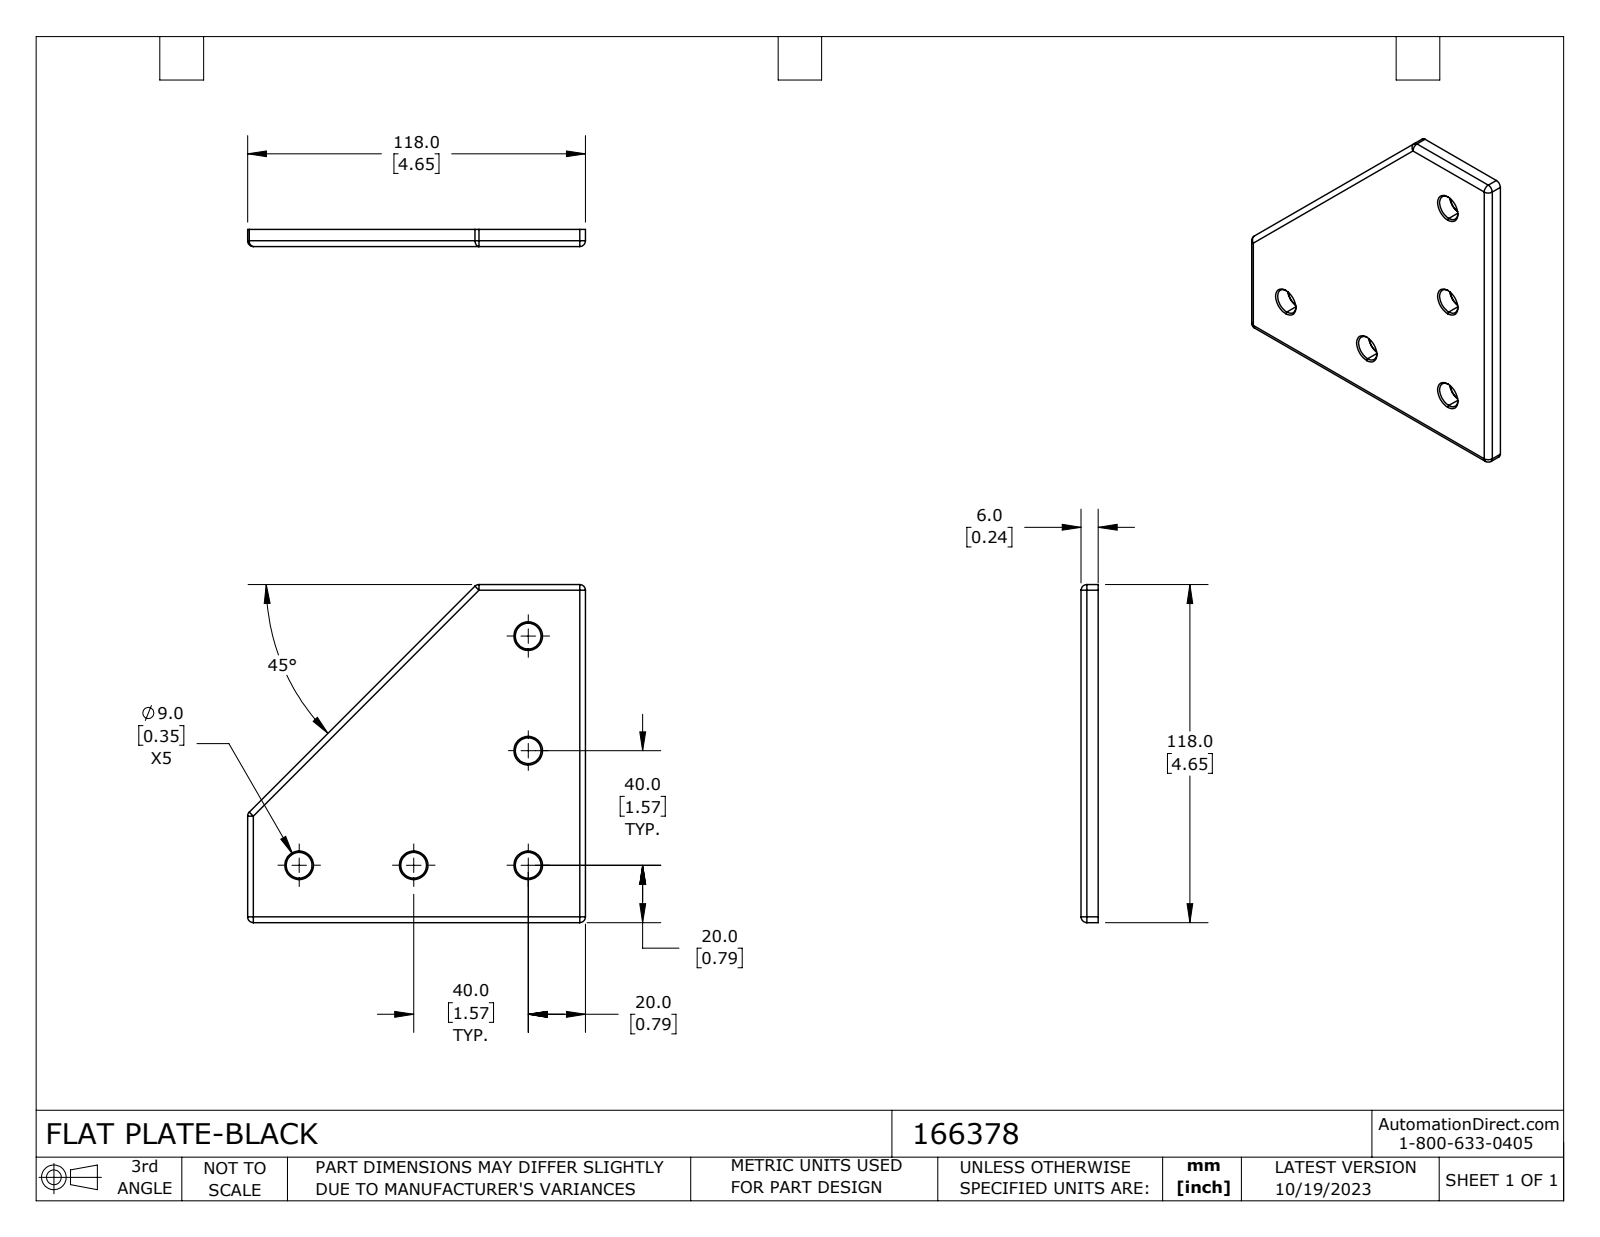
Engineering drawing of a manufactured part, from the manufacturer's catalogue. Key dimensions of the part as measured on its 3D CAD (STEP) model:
Part name (STEP PRODUCT): 166378
STEP written by: SolidWorks 2023 (CONFIG_CONTROL_DESIGN)
Units: millimetres
Bodies: 1 solid, 52 faces (7 planar, 20 cylindrical, 25 other)
Overall size (bounding box): 118 × 118 × 6
Volume: 62 022 mm³ · Surface area: 23 745 mm²
Round holes (diameter × count): ⌀9 ×5
Partial cylindrical surfaces — rounded edges, fillets, slot ends (radius × count): R2 ×10
Main face-to-face distances: 6, 118
Hole centre spacings: 40, 80, 89.44, 56.57, 113.14
